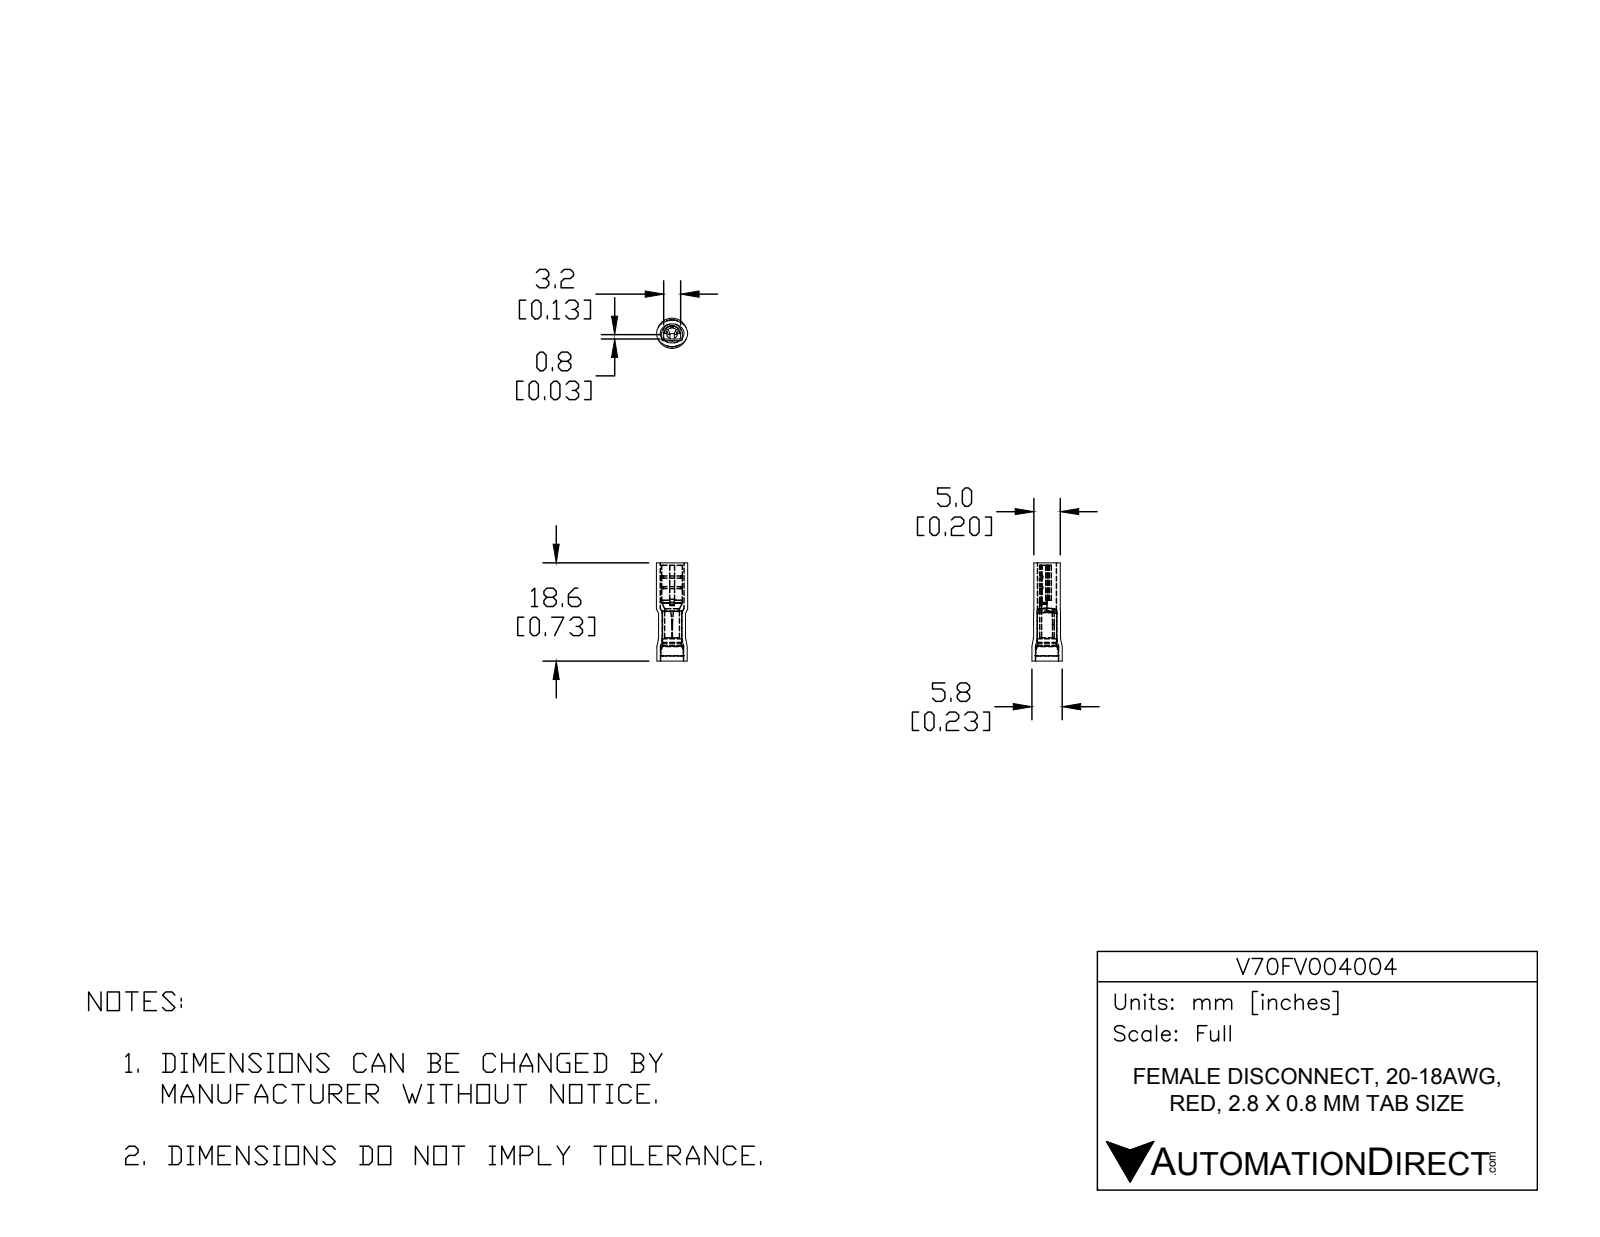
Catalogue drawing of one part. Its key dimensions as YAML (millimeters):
part_name: "V70FV004004"
step_written_by: "SolidWorks 2017 (AUTOMOTIVE_DESIGN)"
units: millimeters
bodies: {solids: 3, faces: 127, planar: 51, cylindrical: 36, other: 40}
overall_size: [18.6, 5.9, 5.75]
volume: 264
surface_area: 1014
round_holes:
  - {diameter: 2.08, count: 1}
  - {diameter: 2.98, count: 1}
  - {diameter: 3.7, count: 1}
  - {diameter: 4.35, count: 1}
round_bosses_or_shafts:
  - {diameter: 5.75, count: 1}
  - {diameter: 5.1, count: 1}
  - {diameter: 3.68, count: 1}
  - {diameter: 2.78, count: 1}
partial_cylinders:
  - {radius: 0.12, count: 2}
  - {radius: 0.25, count: 2}
  - {radius: 0.37, count: 2}
  - {radius: 0.72, count: 2}
  - {radius: 15.72, count: 2}
  - {radius: 0.34, count: 1}
  - {radius: 0.69, count: 1}
face_to_face_distances: [0.35, 3.55, 18.6, 3.9, 3.2, 2, 4.4, 13.7, 9.48, 9.12]
